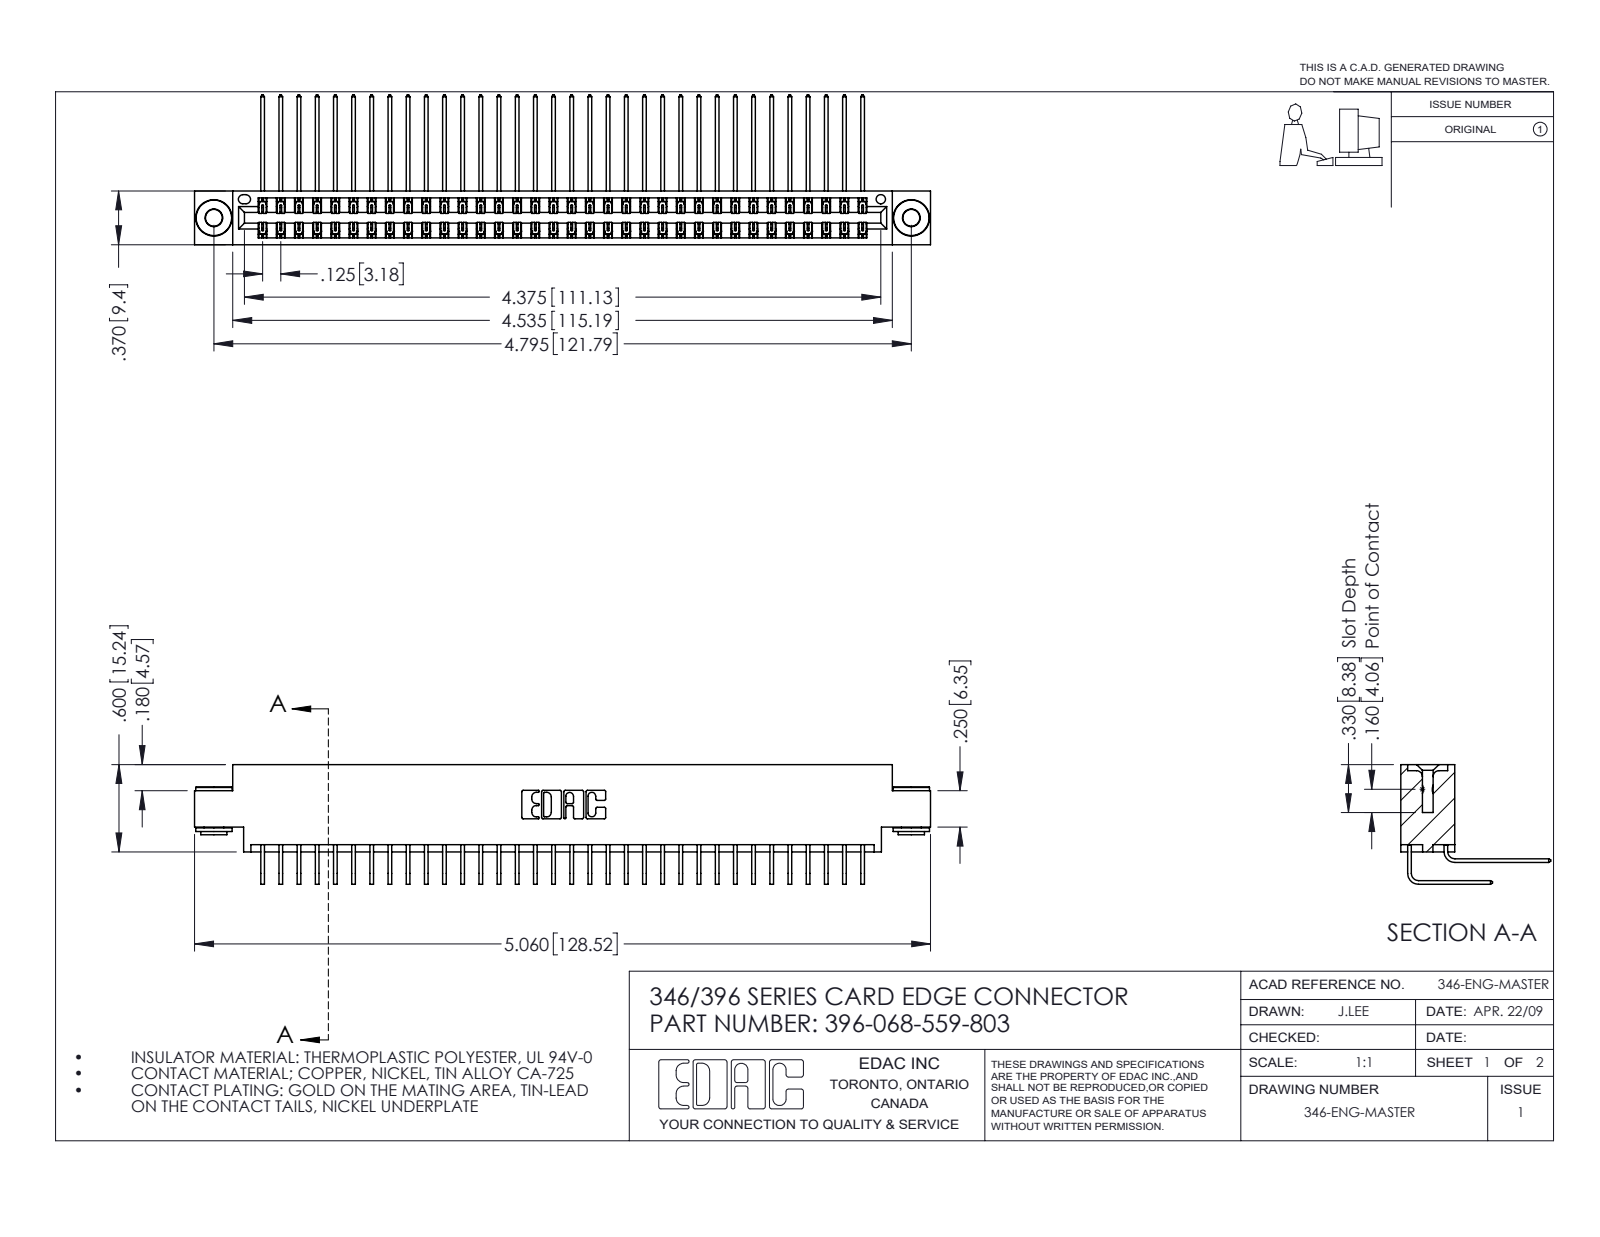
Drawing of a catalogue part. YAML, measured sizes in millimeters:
part_name: "346 Part_0.170 Offset - 0.156 Dia-TH; 396-068-559-803; 345-250-002_345-250-002-102; 345-292-001_559 Tail - 2 (+1 more)"
step_written_by: "SolidWorks 2016 (CONFIG_CONTROL_DESIGN)"
units: millimeters
bodies: {solids: 71, faces: 3836, planar: 2606, cylindrical: 1222, other: 8}
overall_size: [128.5, 26.2, 20.9]
volume: 12700
surface_area: 19650
round_holes:
  - {diameter: 2.9, count: 2}
  - {diameter: 4, count: 2}
  - {diameter: 1.6, count: 1}
round_bosses_or_shafts:
  - {diameter: 6.4, count: 2}
  - {diameter: 4.6, count: 2}
  - {diameter: 3.5, count: 2}
partial_cylinders:
  - {radius: 0.2, count: 102}
  - {radius: 0.3, count: 22}
  - {radius: 0.2, count: 6}
  - {radius: 0.8, count: 6}
  - {radius: 0.7, count: 3}
  - {radius: 0.4, count: 2}
  - {radius: 0.6, count: 2}
  - {radius: 0.6, count: 2}
face_to_face_distances: [1.2, 8.2, 0.6, 9.4, 6.4, 1.8, 7.6, 7, 3.8, 3.8]
hole_center_spacings: [6.2, 116.5, 121.8]
